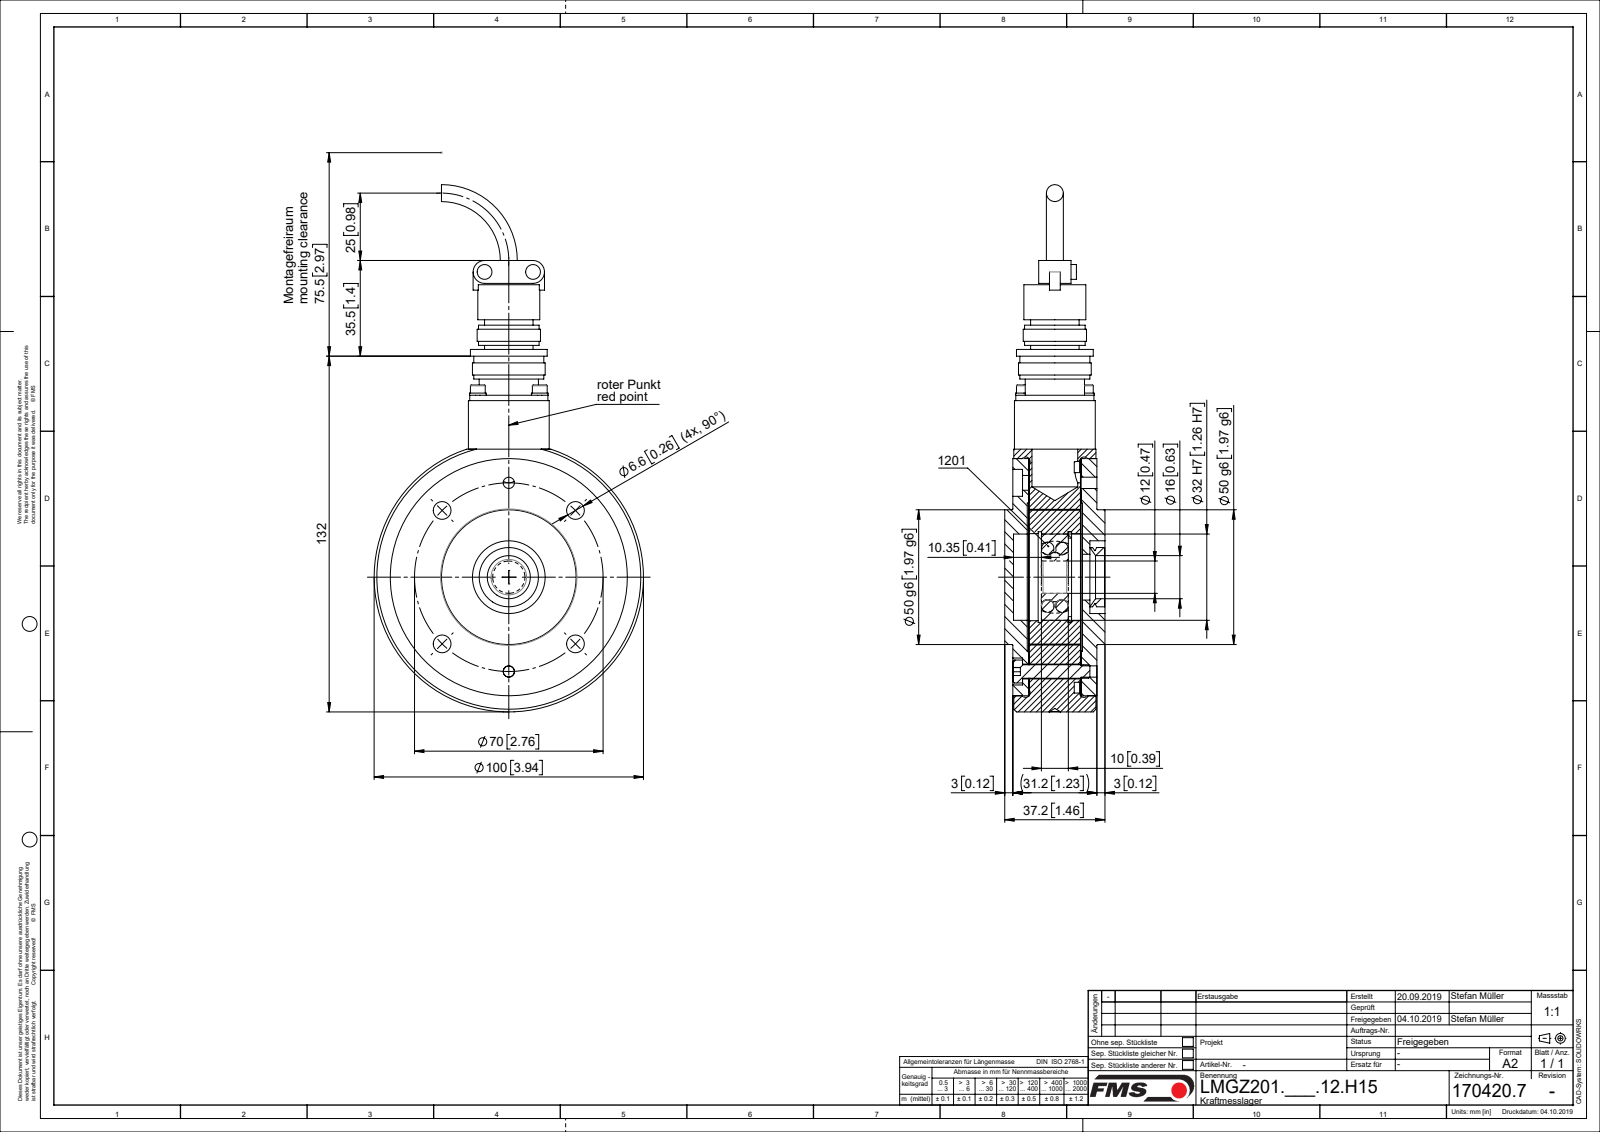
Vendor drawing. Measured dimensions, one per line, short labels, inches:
name: L1704207; L4866604; TEIL1; L48891 (+8 more)
written by: Mechanical Desktop 2009 (CONFIG_CONTROL_DESIGN)
unit: in
bodies: 18 solids, 325 faces (92 planar, 199 cylindrical, 34 other)
size: 7.703 × 3.937 × 1.465
volume: 16.2 in³; area: 146.4 in²
holes: 4× ⌀0.102, 4× ⌀0.126, 4× ⌀0.134, 4× ⌀0.26, 2× ⌀0.217, 1× ⌀0.472, 1× ⌀0.63, 1× ⌀0.669, 1× ⌀0.906, 1× ⌀1, 1× ⌀1.063, 1× ⌀1.26
bosses: 6× ⌀0.217, 4× ⌀0.244, 4× ⌀0.118, 4× ⌀0.098, 2× ⌀0.866, 1× ⌀3.937, 1× ⌀3.465, 1× ⌀1.969
rounds: 2× R0.167
face distances: 0.758, 0.748, 0.23, 0.988, 0.24, 0.998, 0.768, 0.217, 0.974, 0.787
hole spacings: 1.378, 0.64, 0.906, 1.055, 1.949, 2.546, 2.756, 1.281
